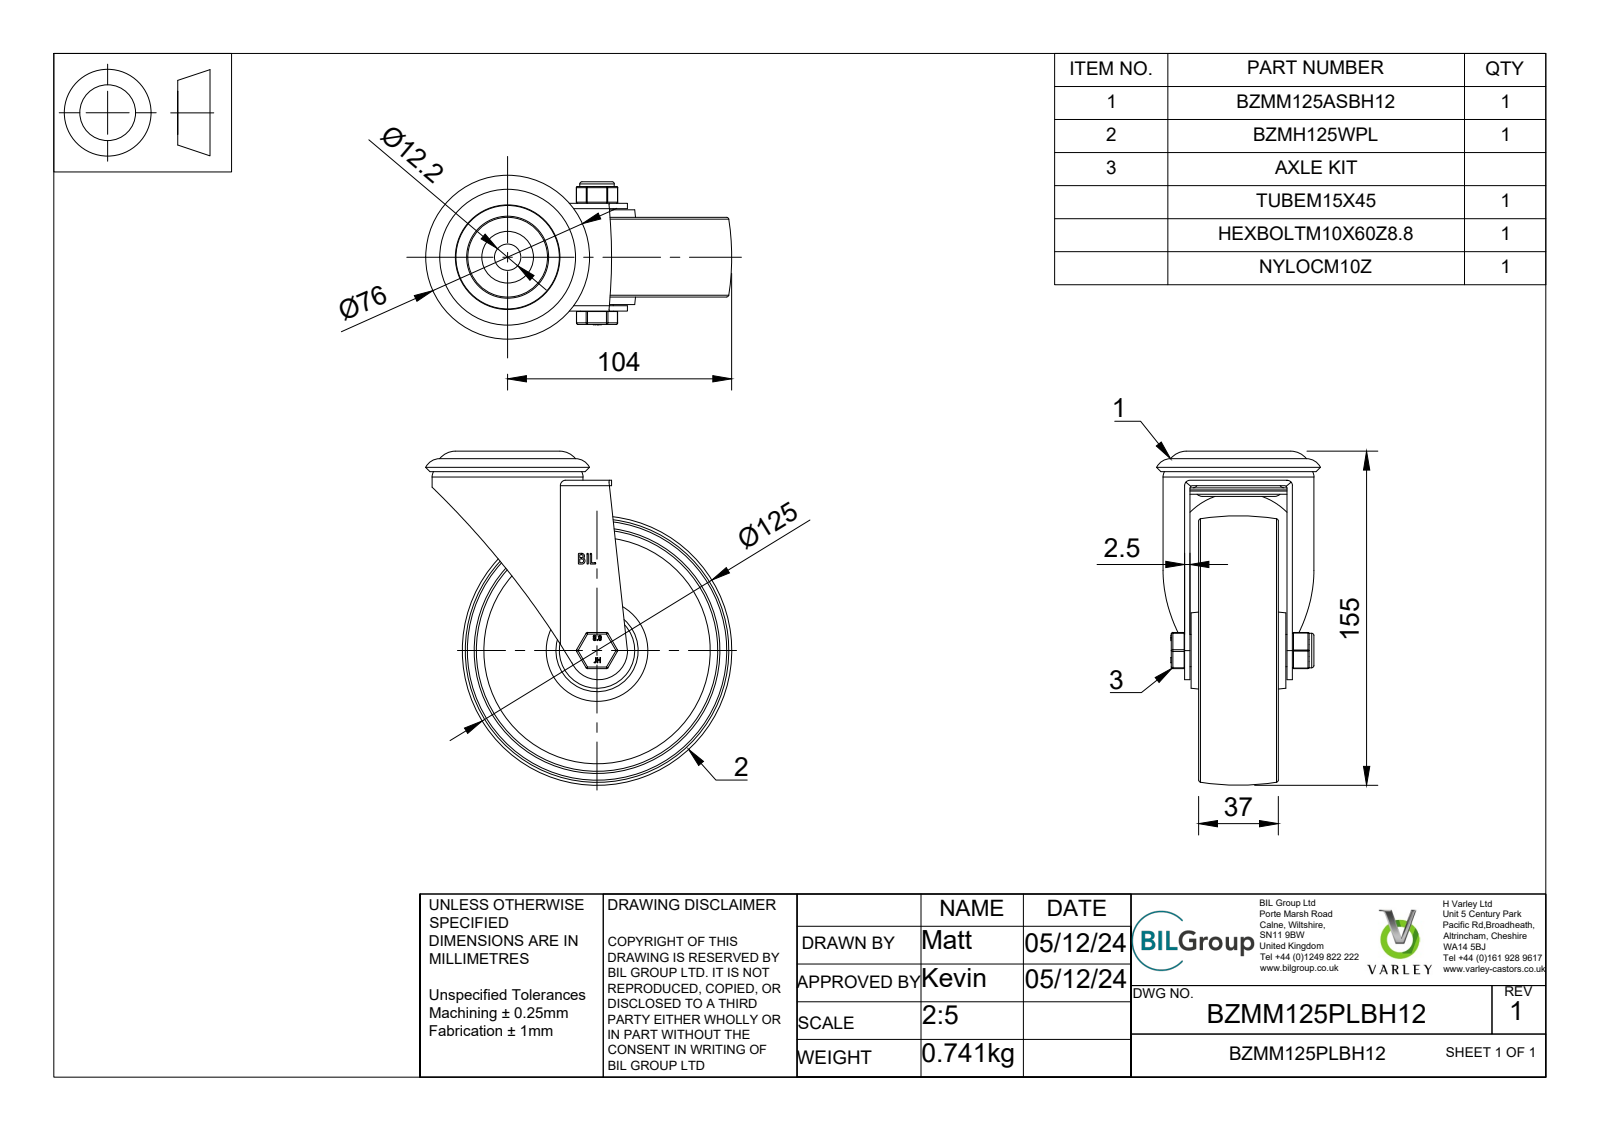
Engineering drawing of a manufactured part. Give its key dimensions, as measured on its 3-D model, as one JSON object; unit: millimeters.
{"part_name": "BZMM125PLBH12 v3; BZMM125ASBH12 v1; ZINC PLATED, PRESSED STEEL HEAD; ZINC PLATED, PRESSED STEEL FORKS (+8 more)", "step_written_by": "Autodesk Translation Framework v13.20.0.188 (AP242_MANAGED_MODEL_BASED_3D_ENGINEERING_MIM_LF)", "units": "millimeters", "bodies": {"solids": 7, "faces": 331, "planar": 115, "cylindrical": 107, "other": 109}, "overall_size": [155, 142, 76], "volume_mm3": 249662, "surface_area_mm2": 108877, "round_holes": [[10, 1], [10.2, 1], [12, 1], [12.2, 1], [15.2, 1], [65, 1], [72, 1], [112, 1]], "round_bosses_or_shafts": [[70, 1], [49.5, 1], [38, 1], [24, 1], [21.31, 1], [16, 1], [15.5, 1], [14.95, 1]], "partial_cylinders_radius": [[0.5, 18], [0.75, 12], [1.25, 4], [2.5, 2], [13.5, 1], [253.62, 1], [408.21, 1]], "face_to_face_distances": [6, 2.5, 28, 22, 47.5, 19.5, 25.5, 6.5, 4, 50]}
